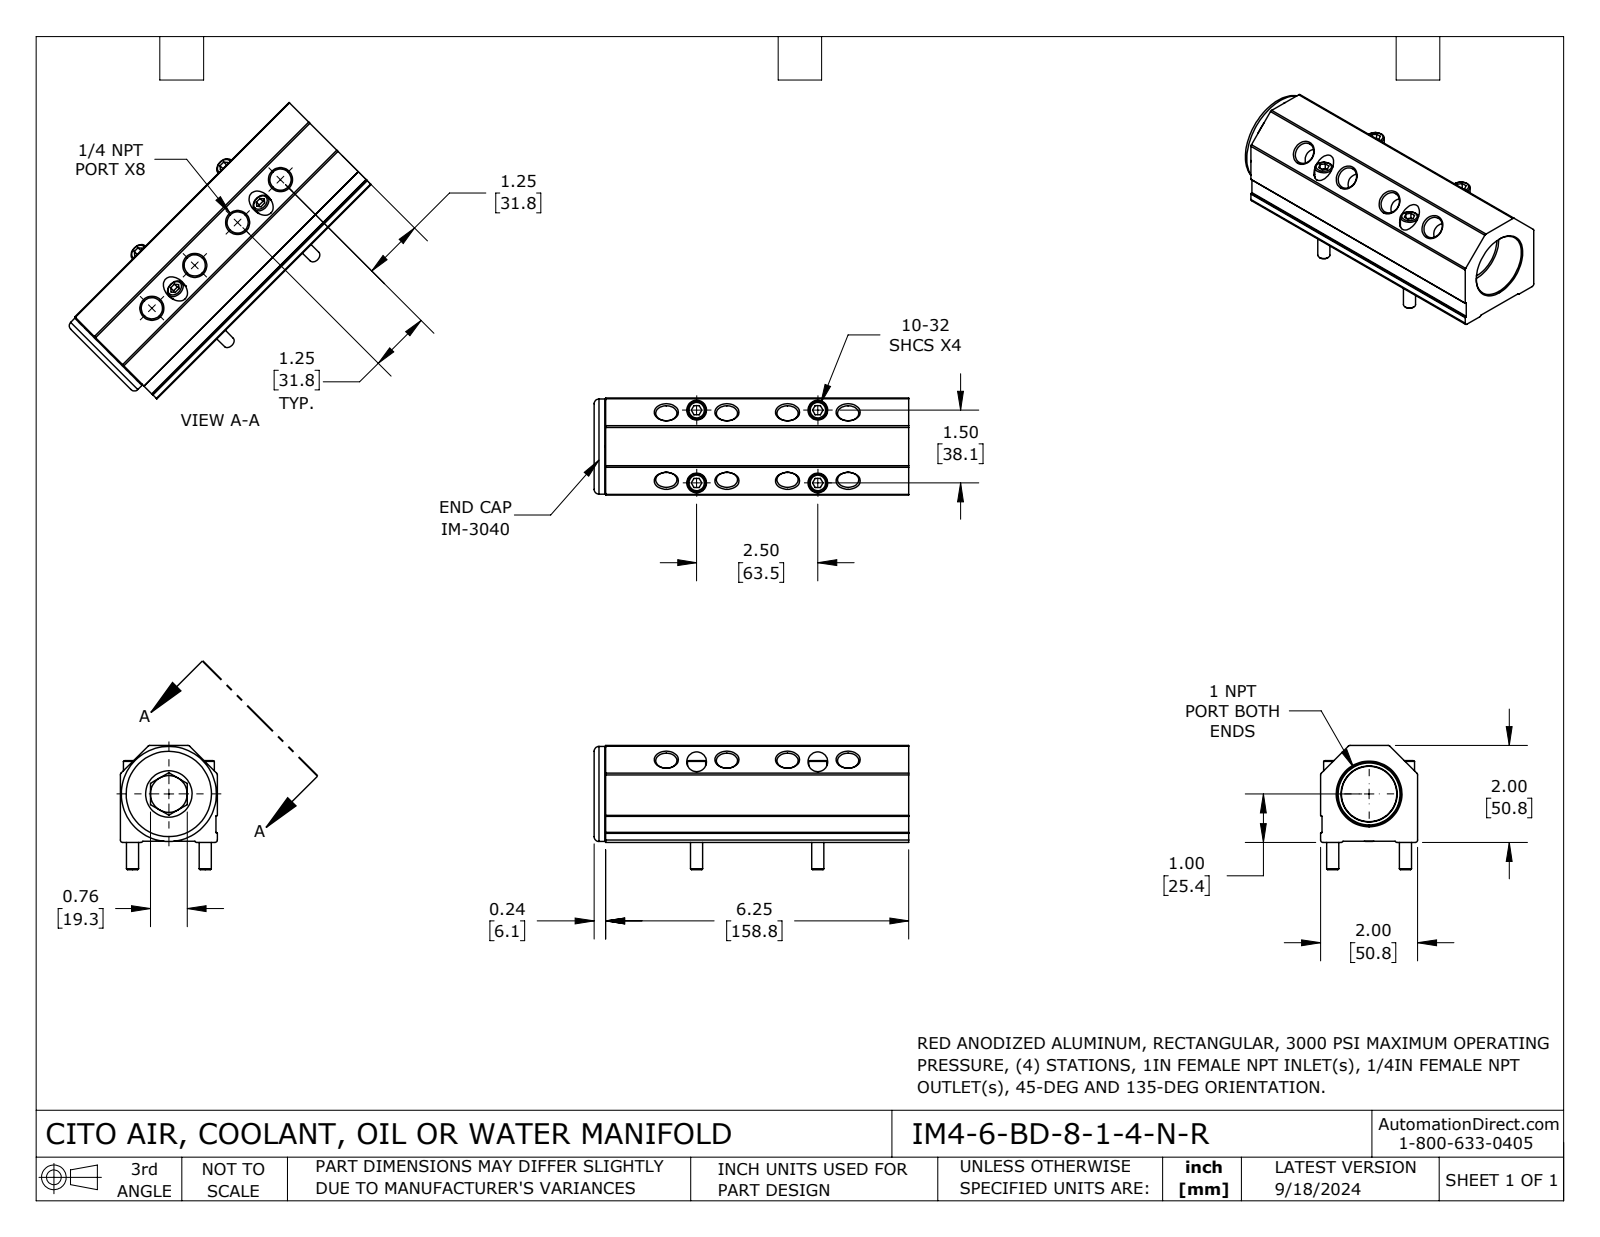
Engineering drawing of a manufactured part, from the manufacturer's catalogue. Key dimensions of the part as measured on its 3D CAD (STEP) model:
Part name (STEP PRODUCT): IM4-6-BD-8-1-4-N-R
STEP written by: SolidWorks 2023 (CONFIG_CONTROL_DESIGN)
Units: inches
Bodies: 6 solids, 213 faces (81 planar, 74 cylindrical, 58 other)
Overall size (bounding box): 6.49 × 2.56 × 2
Volume: 16.22 in³ · Surface area: 101.9 in²
Round holes (diameter × count): ⌀0.437 ×8, ⌀0.266 ×4, ⌀0.406 ×4, ⌀0.758 ×1, ⌀1.156 ×1, ⌀1.637 ×1
Round bosses / shafts (diameter × count): ⌀0.375 ×4, ⌀0.25 ×4, ⌀1.96 ×1, ⌀1.359 ×1, ⌀1.293 ×1, ⌀1.14 ×1
Partial cylindrical surfaces — rounded edges, fillets, slot ends (radius × count): R0.05 ×8, R0.01 ×4
Main face-to-face distances: 2, 1.975, 0.025, 6.25, 0.028, 1.972, 0.24, 6.49, 0.764, 0.524
Hole centre spacings: 1.25, 2.5, 1.5, 2.915, 3.75
